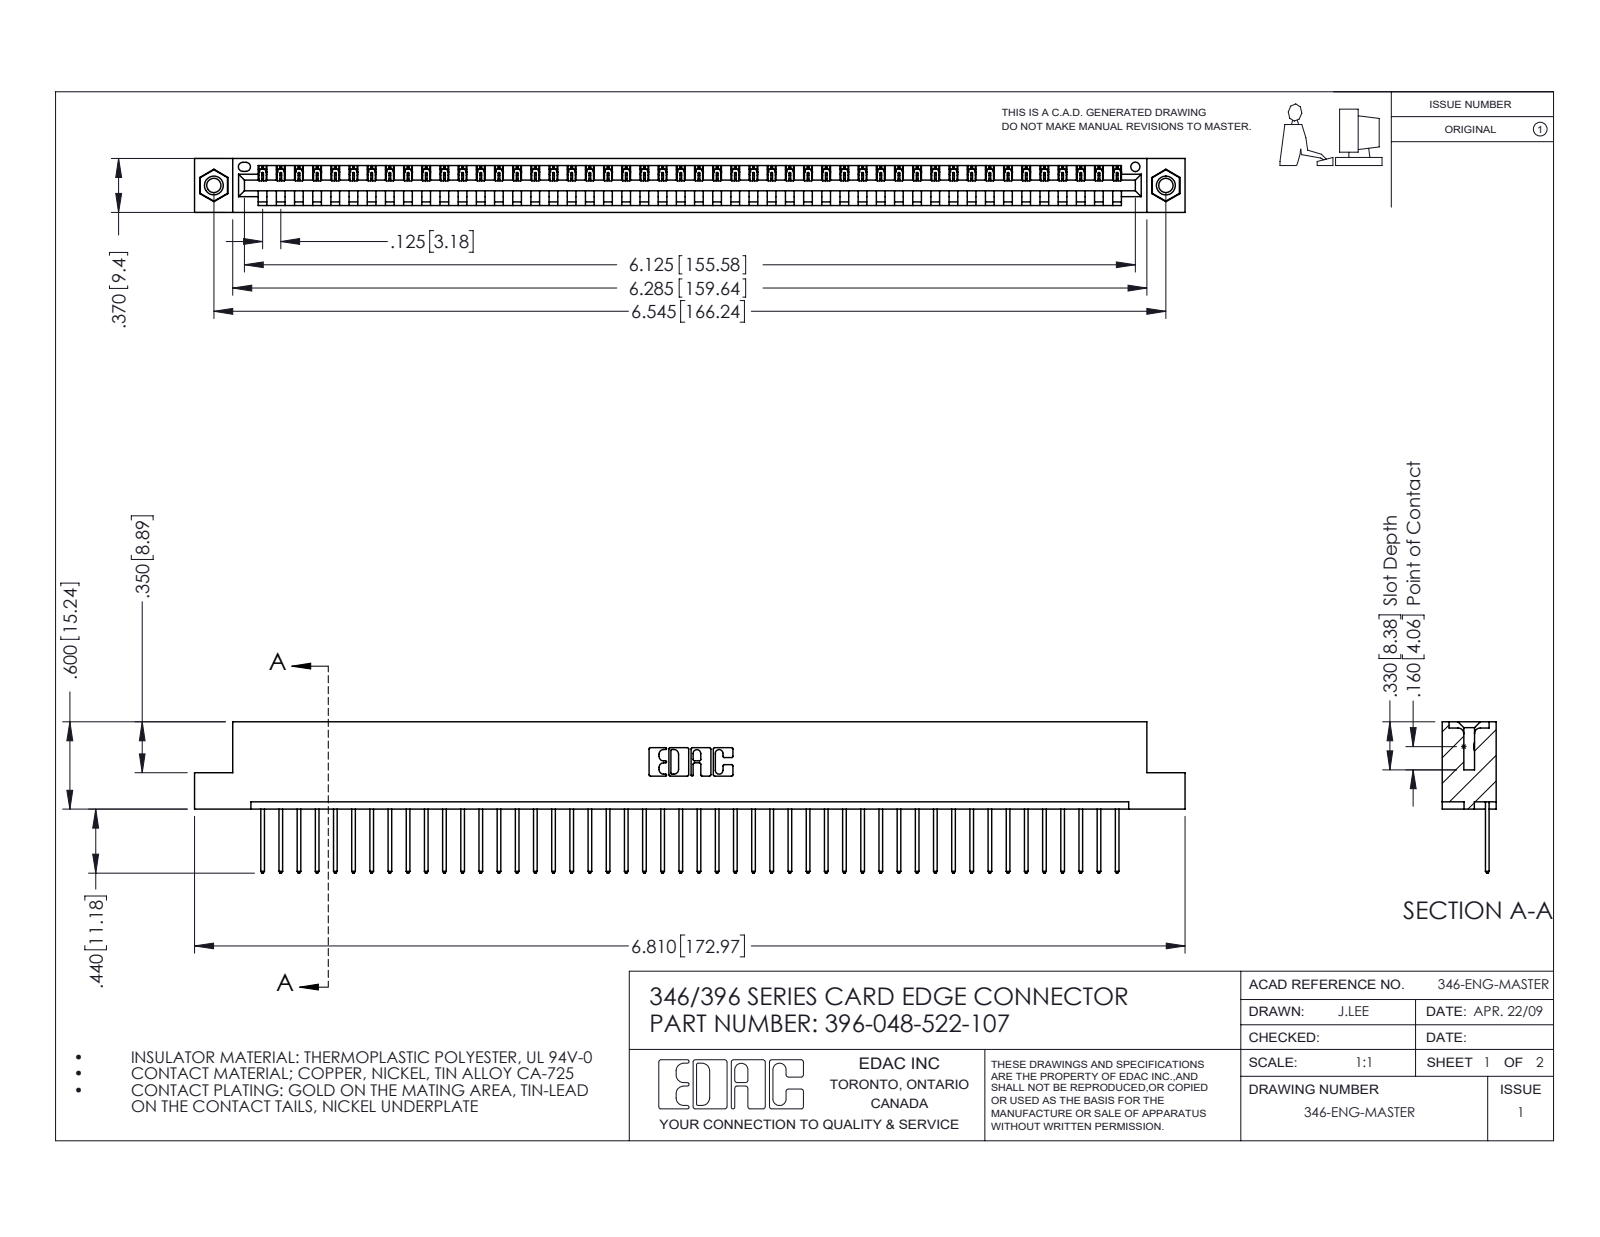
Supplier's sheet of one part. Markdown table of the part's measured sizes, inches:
| quantity | value |
| --- | --- |
| part name | 396-048-522-107; 345-292-001_345-293-122; 346 Part_Flush Mounting Lugs - 0.156 Dia-TI; 345-250-001_345-250-005-103 |
| STEP written by | SolidWorks 2016 (CONFIG_CONTROL_DESIGN) |
| units | inches |
| bodies | 51 solids, 2966 faces (2028 planar, 922 cylindrical, 16 other) |
| overall size | 6.81 × 1.04 × 0.37 |
| volume | 1.012 in³ |
| surface area | 32.57 in² |
| round holes (diameter × count) | 0.098 × 2, 0.125 × 2, 0.156 × 2, 0.064 × 1 |
| round bosses / shafts (diameter × count) | 0.155 × 2 |
| partial cylindrical surfaces (radius × count) | 0.006 × 96, 0.01 × 96, 0.01 × 22, 0.007 × 6, 0.031 × 6, 0.026 × 3, 0.031 × 2, 0.04 × 2 |
| main face-to-face distances | 0.048, 0.322, 0.37, 0.25, 0.072, 0.298, 0.025, 0.148, 0.222, 0.1 |
| hole center spacings | 0.246, 6.336, 6.545 |
